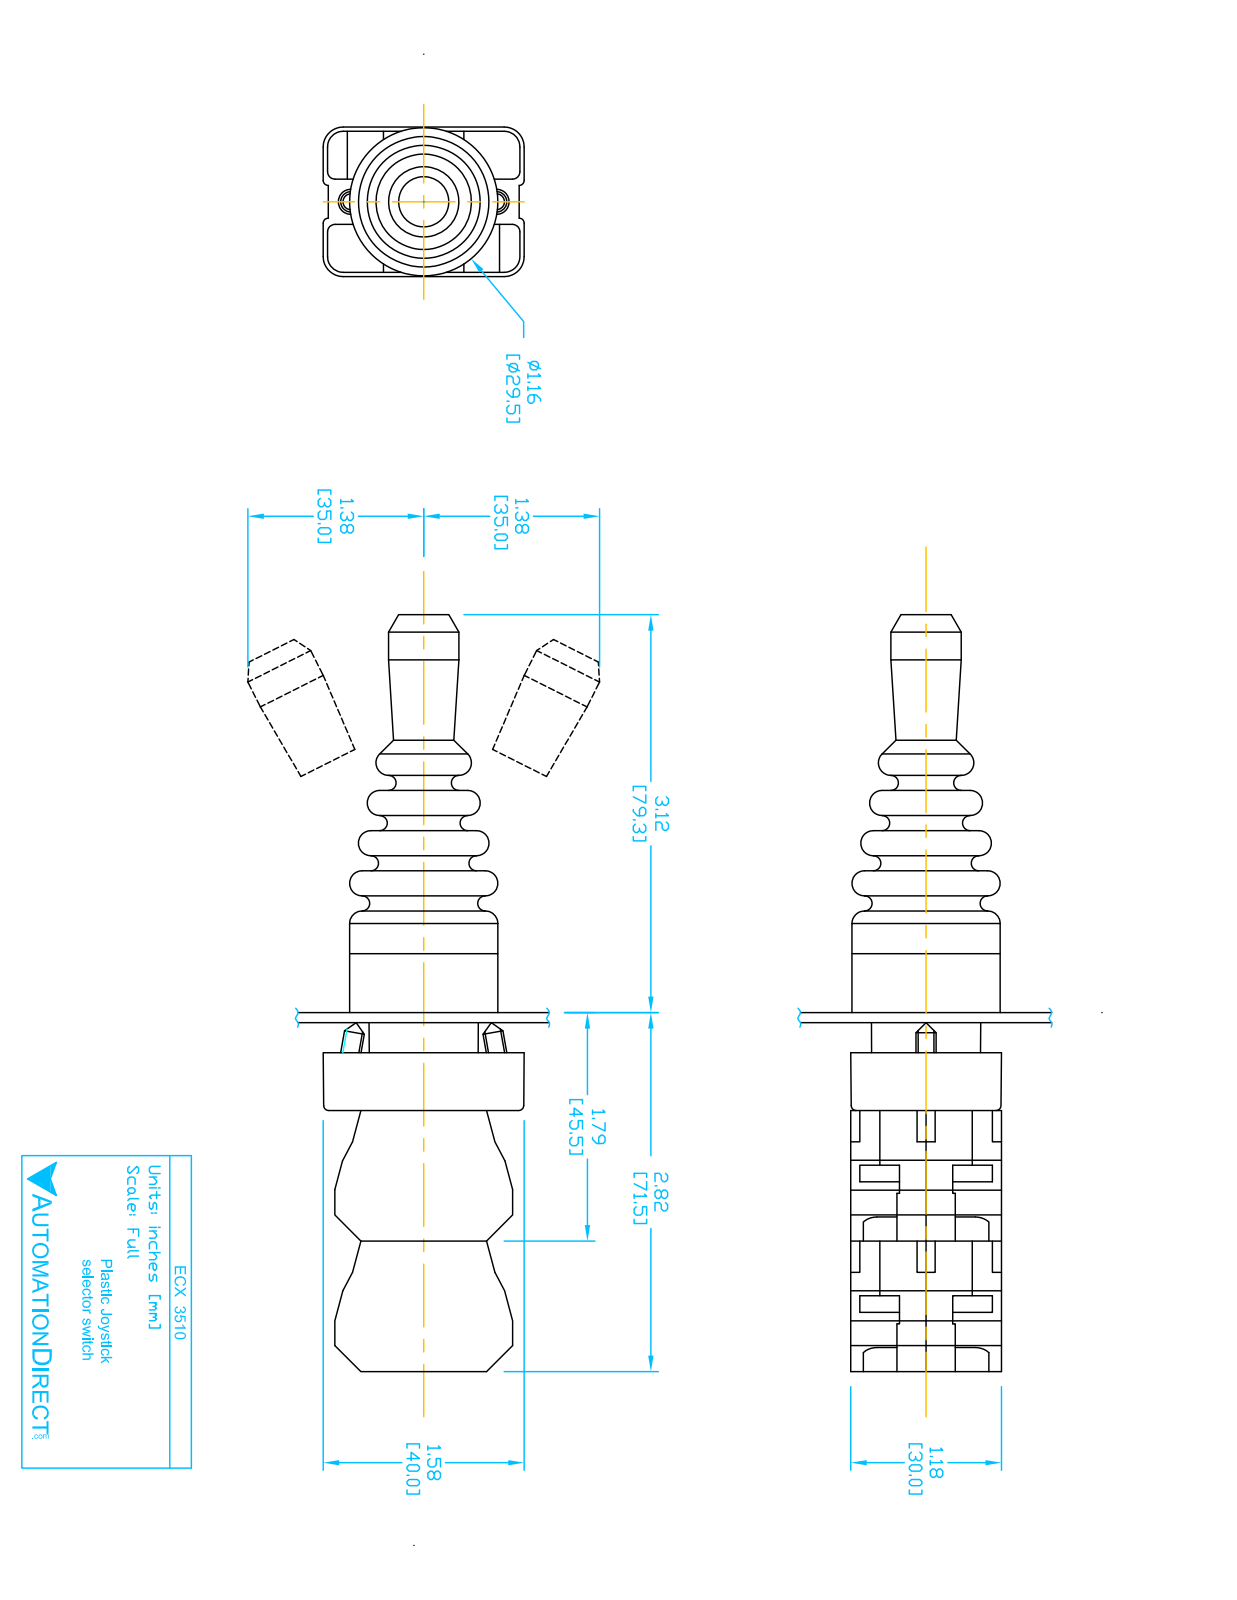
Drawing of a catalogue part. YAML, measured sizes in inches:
part_name: "ECX3510"
step_written_by: "SolidWorks 2017 (AUTOMOTIVE_DESIGN)"
units: inches
bodies: {solids: 7, faces: 521, planar: 300, cylindrical: 144, other: 77}
overall_size: [4.886, 1.581, 1.181]
volume: 3.568
surface_area: 37.85
round_holes:
  - {diameter: 0.079, count: 4}
  - {diameter: 0.087, count: 2}
  - {diameter: 0.124, count: 2}
  - {diameter: 0.13, count: 2}
  - {diameter: 0.197, count: 1}
  - {diameter: 0.878, count: 1}
  - {diameter: 0.888, count: 1}
round_bosses_or_shafts:
  - {diameter: 0.157, count: 2}
  - {diameter: 1.181, count: 1}
  - {diameter: 1.175, count: 1}
  - {diameter: 0.945, count: 1}
  - {diameter: 0.856, count: 1}
  - {diameter: 0.78, count: 1}
partial_cylinders:
  - {radius: 0.059, count: 24}
  - {radius: 0.041, count: 12}
  - {radius: 0.124, count: 12}
  - {radius: 0.157, count: 12}
  - {radius: 0.039, count: 4}
  - {radius: 0.02, count: 2}
  - {radius: 0.063, count: 2}
  - {radius: 0.079, count: 2}
face_to_face_distances: [0.579, 0.598, 1.193, 1.177, 0.02, 0.031, 0.033, 1.024, 2.217, 1.055]
hole_center_spacings: [0.236, 0.98, 0.472, 0.544, 1.004, 1.013, 0.49, 0.491]
